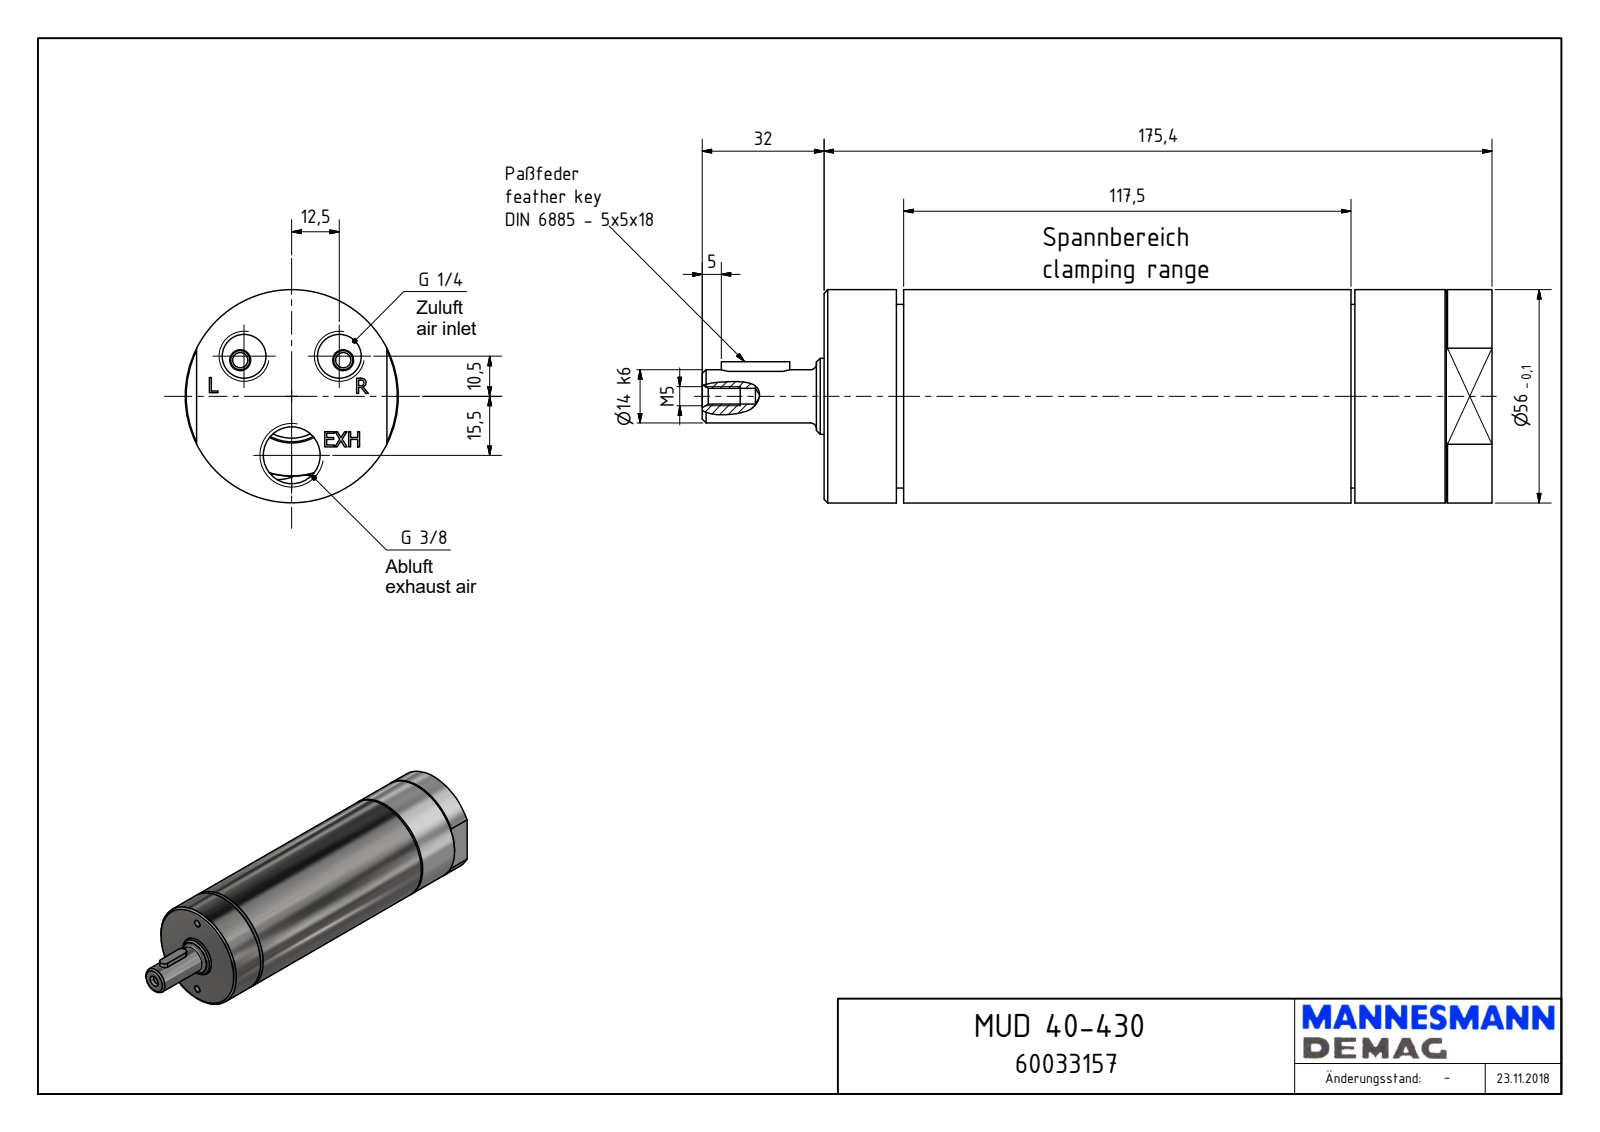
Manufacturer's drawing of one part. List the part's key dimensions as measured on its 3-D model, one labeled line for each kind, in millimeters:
Part name (STEP PRODUCT): MUD 40-430_60033157
STEP written by: Autodesk Inventor 2018 (AUTOMOTIVE_DESIGN)
Units: millimetres
Bodies: 1 solid, 171 faces (92 planar, 32 cylindrical, 47 other)
Overall size (bounding box): 207.4 × 56 × 56
Volume: 429 585 mm³ · Surface area: 44 644 mm²
Round holes (diameter × count): ⌀4 ×2, ⌀11.45 ×2, ⌀4.13 ×1, ⌀14.95 ×1, ⌀21 ×1, ⌀21.25 ×1, ⌀23.54 ×1, ⌀26 ×1, ⌀48.38 ×1
Round bosses / shafts (diameter × count): ⌀56 ×1, ⌀48.18 ×1, ⌀19.95 ×1, ⌀14 ×1
Partial cylindrical surfaces — rounded edges, fillets, slot ends (radius × count): R2.5 ×2, R6 ×2, R19.67 ×1, R23 ×1
Main face-to-face distances: 175.4, 20.9, 138.4, 117.5, 154.5, 37, 139.4, 19, 1.9, 119.4
Hole centre spacings: 16.32, 21, 28.85, 33.89, 5.5, 15.5, 25, 36.5
